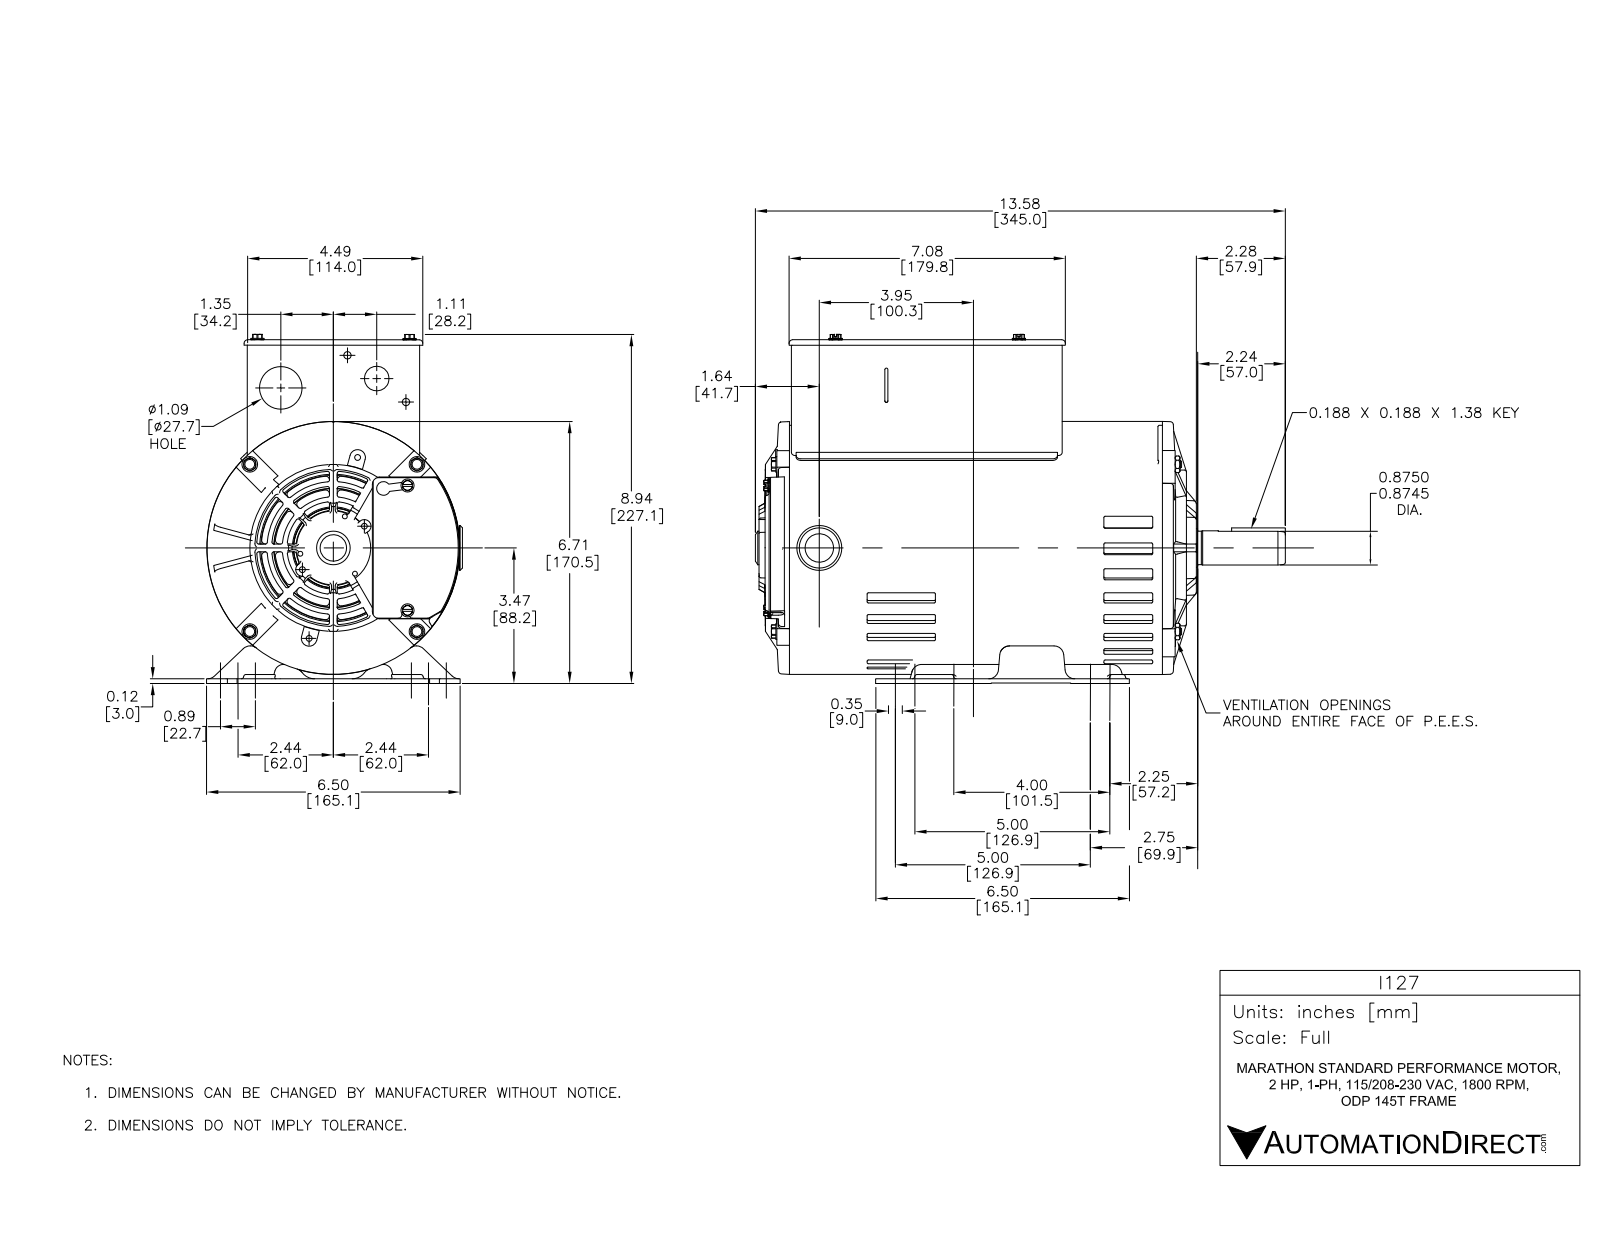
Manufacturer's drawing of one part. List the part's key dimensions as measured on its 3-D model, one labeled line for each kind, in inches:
Part name (STEP PRODUCT): I127 orig mod 1a 100147-956_Rev4 b2b
STEP written by: SolidWorks 2017 (AUTOMOTIVE_DESIGN)
Units: inches
Bodies: 36 solids, 3655 faces (1357 planar, 849 cylindrical, 1449 other)
Overall size (bounding box): 13.584 × 8.946 × 6.558
Volume: 54.31 in³ · Surface area: 1 003 in²
Round holes (diameter × count): ⌀0.22 ×8, ⌀0.31 ×8, ⌀0.188 ×6, ⌀0.153 ×5, ⌀0.147 ×4, ⌀0.15 ×4, ⌀0.193 ×4, ⌀0.25 ×4, ⌀0.345 ×4, ⌀0.125 ×2, ⌀0.144 ×2, ⌀0.345 ×2
Round bosses / shafts (diameter × count): ⌀0.164 ×7, ⌀0.335 ×6, ⌀0.399 ×4, ⌀0.19 ×4, ⌀0.166 ×4, ⌀0.34 ×2, ⌀6.466 ×1, ⌀6.287 ×1
Partial cylindrical surfaces — rounded edges, fillets, slot ends (radius × count): R0.06 ×55, R0.25 ×36, R0.03 ×30, R0.08 ×30, R0.05 ×28, R0.02 ×21, R0.1 ×16, R0.12 ×14
Main face-to-face distances: 0.059, 4.359, 0.044, 4.3, 4.418, 0.119, 6.881, 6.94, 6.822, 0.14
Hole centre spacings: 4.283, 3.027, 3.03, 4.28, 4.285, 6.057, 1.489, 5.213
